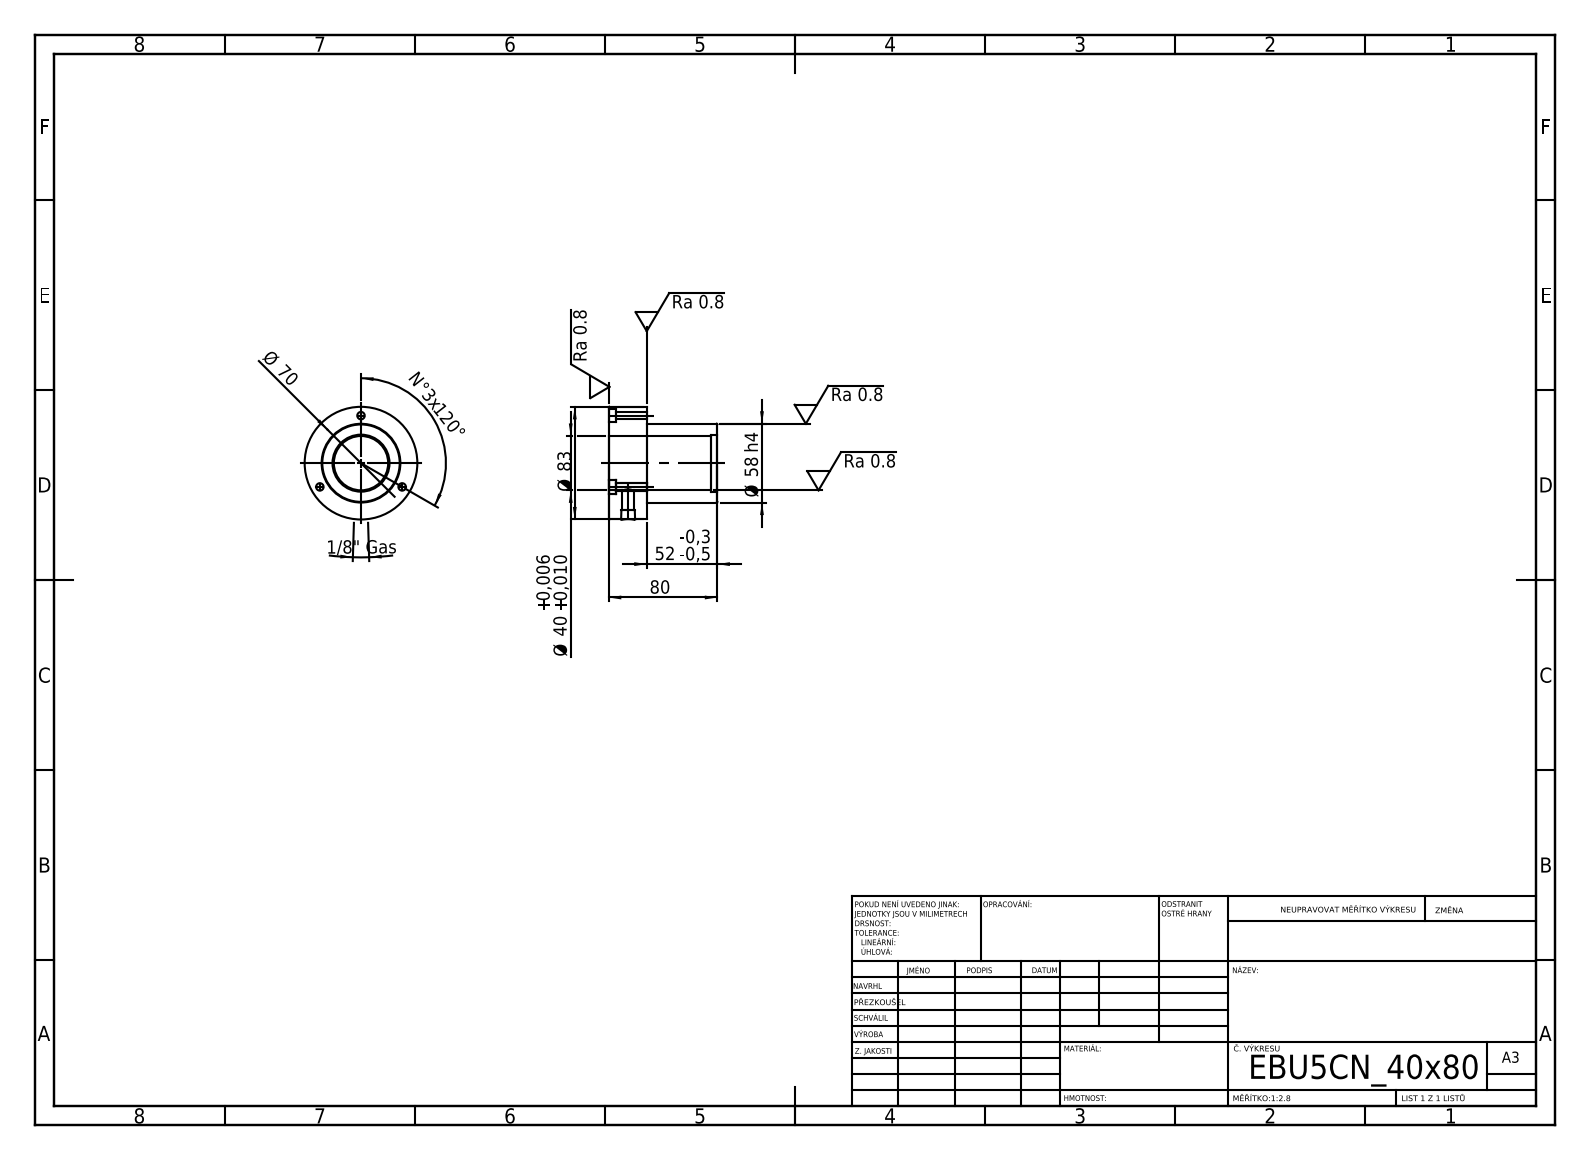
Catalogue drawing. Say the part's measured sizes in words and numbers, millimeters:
Its 3-D file was written by "SolidWorks 2019 (CONFIG_CONTROL_DESIGN)". It is 1 solid with 36 faces: 8 planar, 22 cylindrical and 6 other. Overall it measures 83 by 83 by 80 millimeters. Its volume is 183 405 cubic millimeters and its surface area 37 064 square millimeters. Round holes: 3 of diameter 5.5, 3 of diameter 10, 1 of diameter 8.43, 1 of diameter 40, 1 of diameter 42. Round bosses or shafts: 1 of diameter 83, 1 of diameter 58. The main face-to-face distances are 28, 52, 80, 74.6, 22.6, 5.4, 5, 47, 69.6, 75. The hole center spacings are 35, 60.62.
